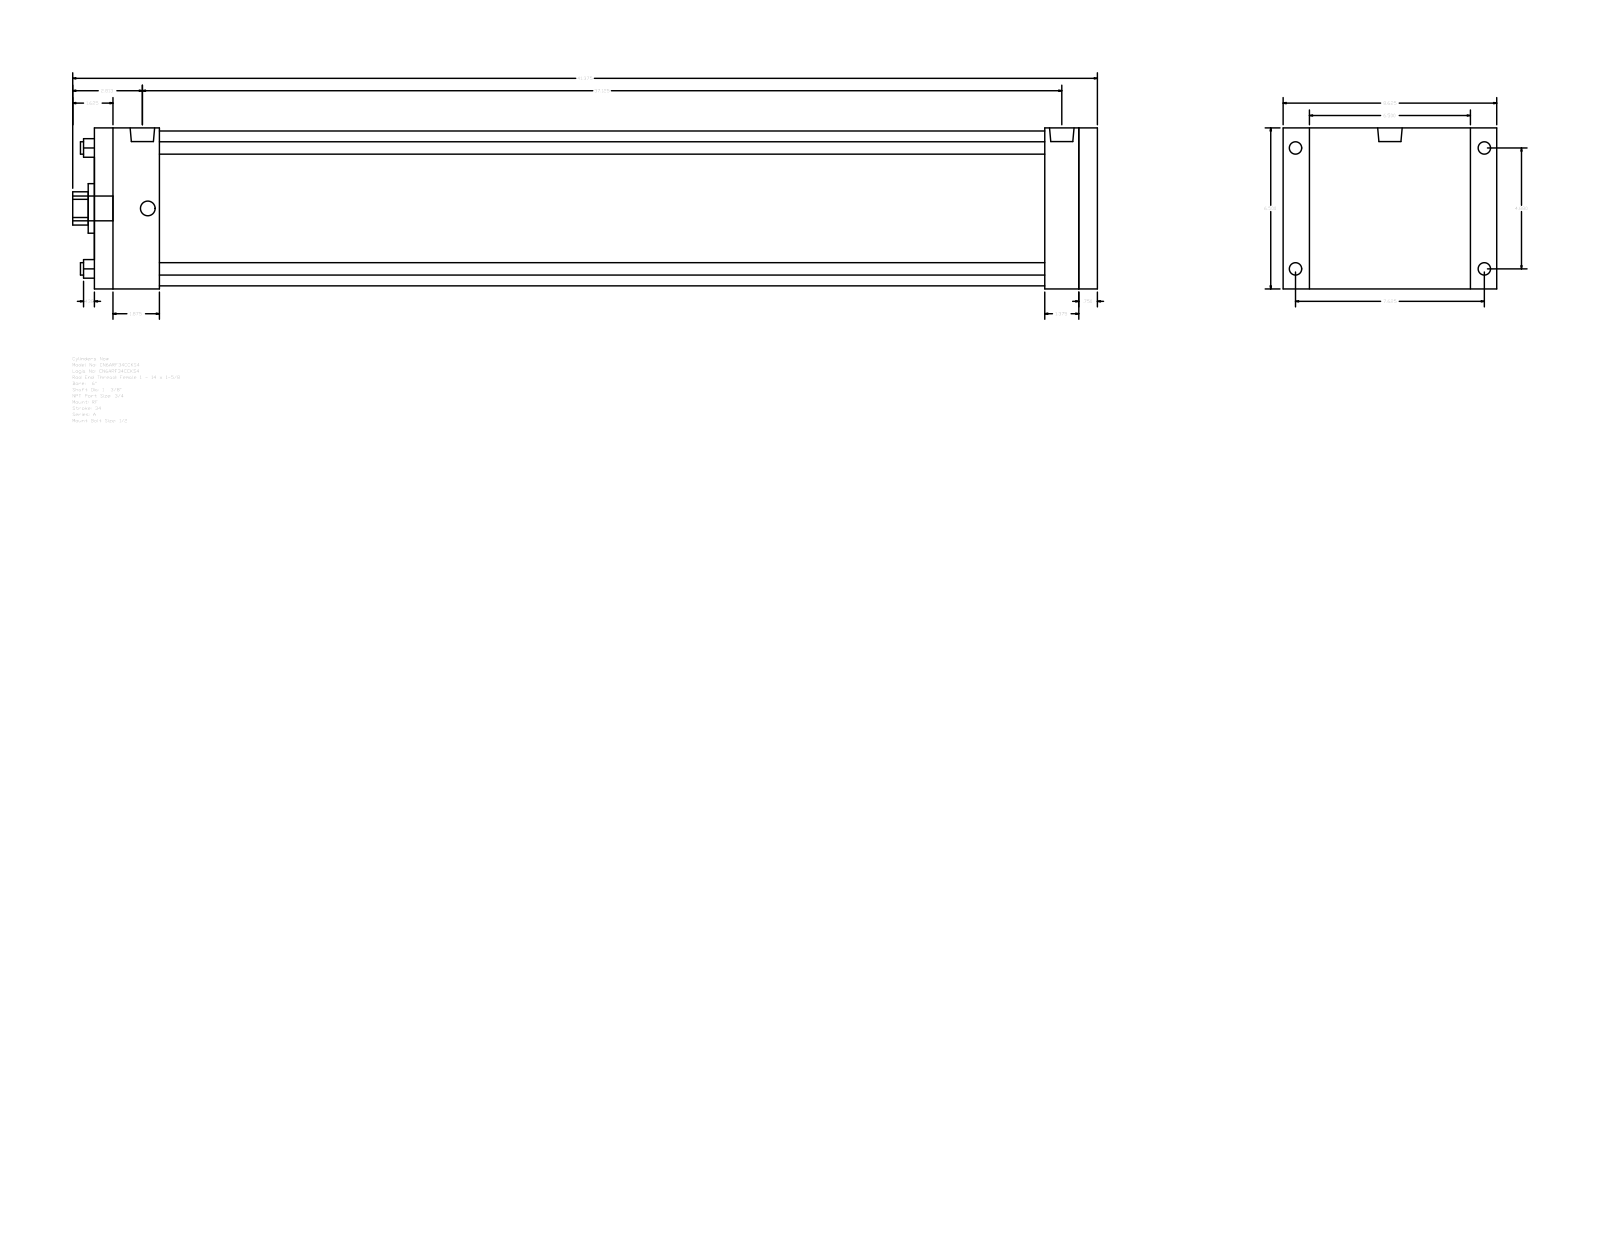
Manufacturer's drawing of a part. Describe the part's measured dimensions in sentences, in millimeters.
The part is named "A_RF__0600_1.375". Its 3-D file was written by "GSSL Pune (CONFIG_CONTROL_DESIGN)". It is 0 solids with 92 faces: 64 planar, 28 cylindrical and 0 other. Overall it measures 1050.92 by 219.07 by 165.1 millimeters. Round holes: 4 of diameter 12.7, 1 of diameter 34.92, 1 of diameter 50.8, 1 of diameter 158.75. Round bosses or shafts: 4 of diameter 15.08, 4 of diameter 12.7, 2 of diameter 25.12, 1 of diameter 25.4. Partial cylindrical surfaces (rounded edges, fillets, slot ends): 1 of radius 17.06. The main face-to-face distances are 165.1, 1028.69, 19.04, 1009.65, 66.67, 942.98, 962.02, 974.72, 908.05, 34.93. The hole center spacings are 87.65, 123.96, 175.31.
